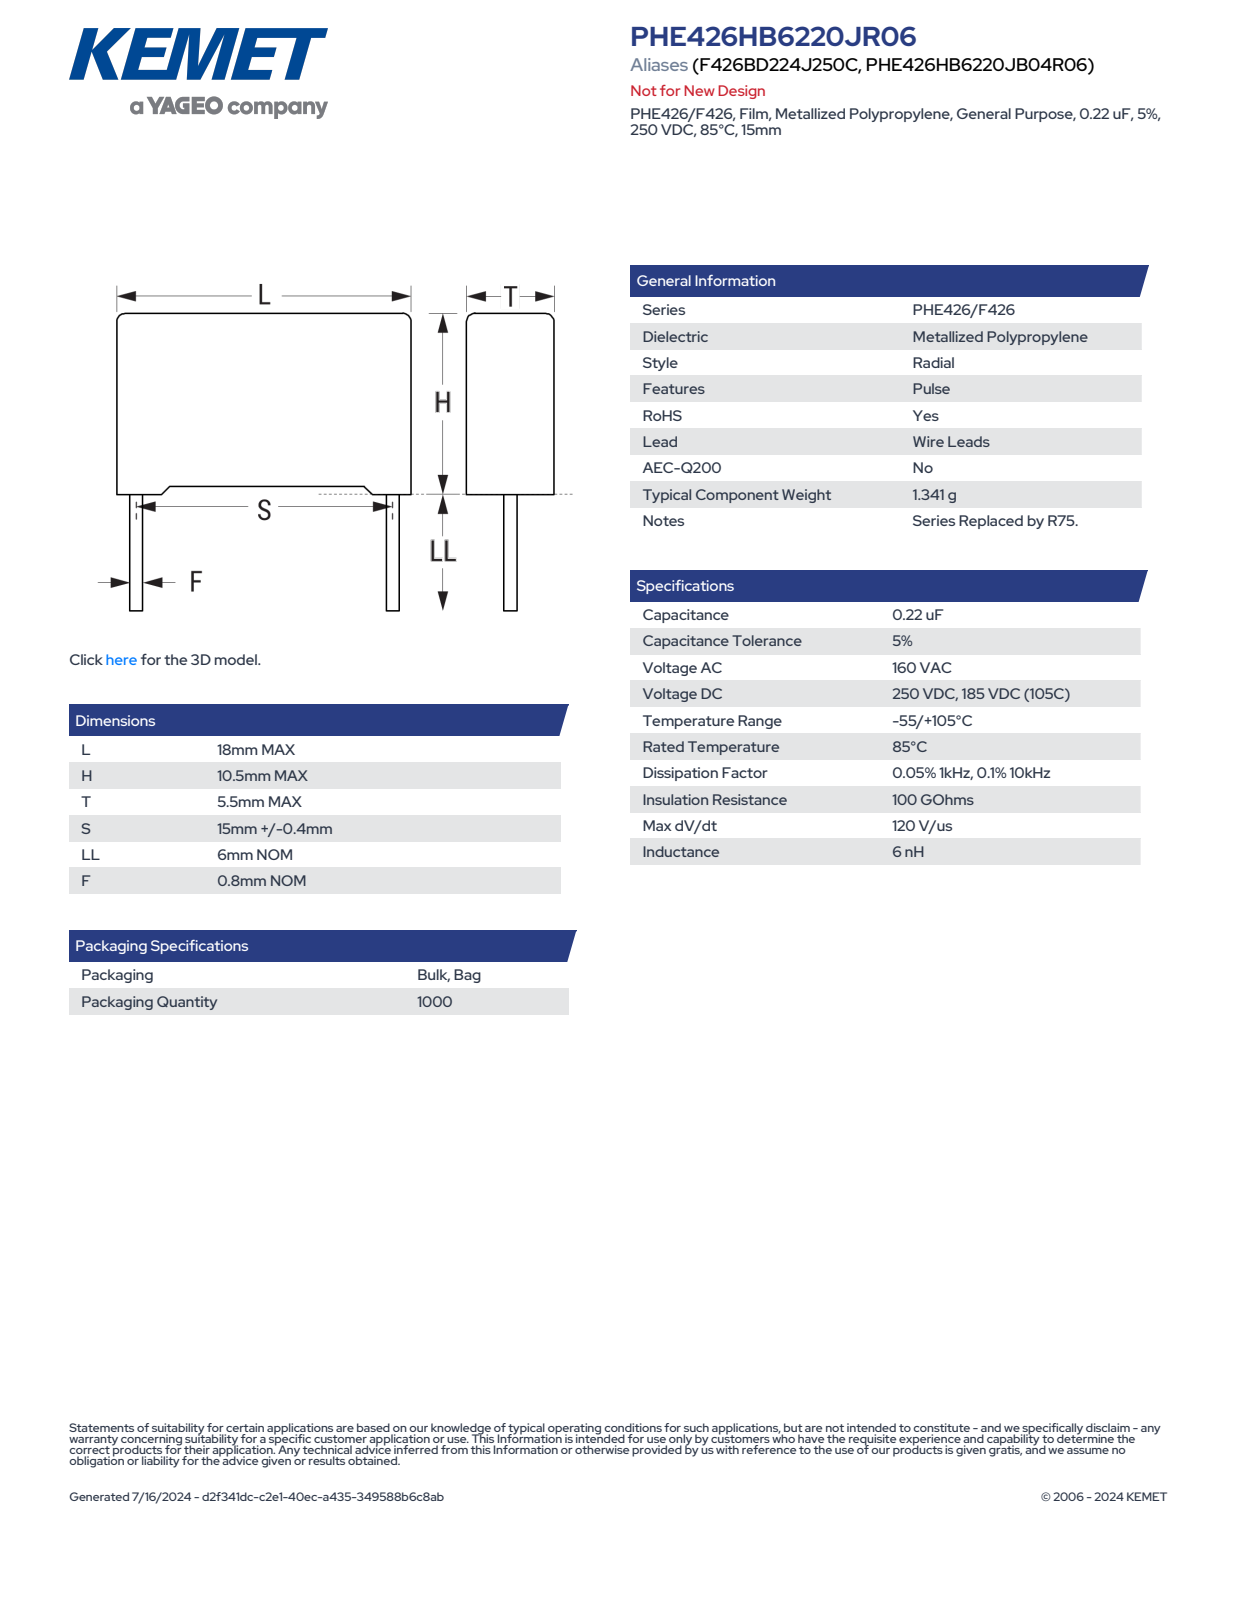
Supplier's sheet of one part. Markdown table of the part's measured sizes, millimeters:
| quantity | value |
| --- | --- |
| part name | CFR_RB2_18X10.5X5.5_L18H10.5T5.5S15LL6F0.8 |
| STEP written by | SolidWorks 2021 (AUTOMOTIVE_DESIGN) |
| units | millimeters |
| bodies | 4 solids, 85 faces (77 planar, 8 cylindrical, 0 other) |
| overall size | 18 × 16.5 × 5.5 |
| volume | 985 mm³ |
| surface area | 755 mm² |
| round bosses / shafts (diameter × count) | 0.8 × 2 |
| partial cylindrical surfaces (radius × count) | 0.5 × 4 |
| main face-to-face distances | 5.5, 9.75, 18, 0.6, 4.9, 0.39, 10.14, 0.75, 0.36, 10.5 |
